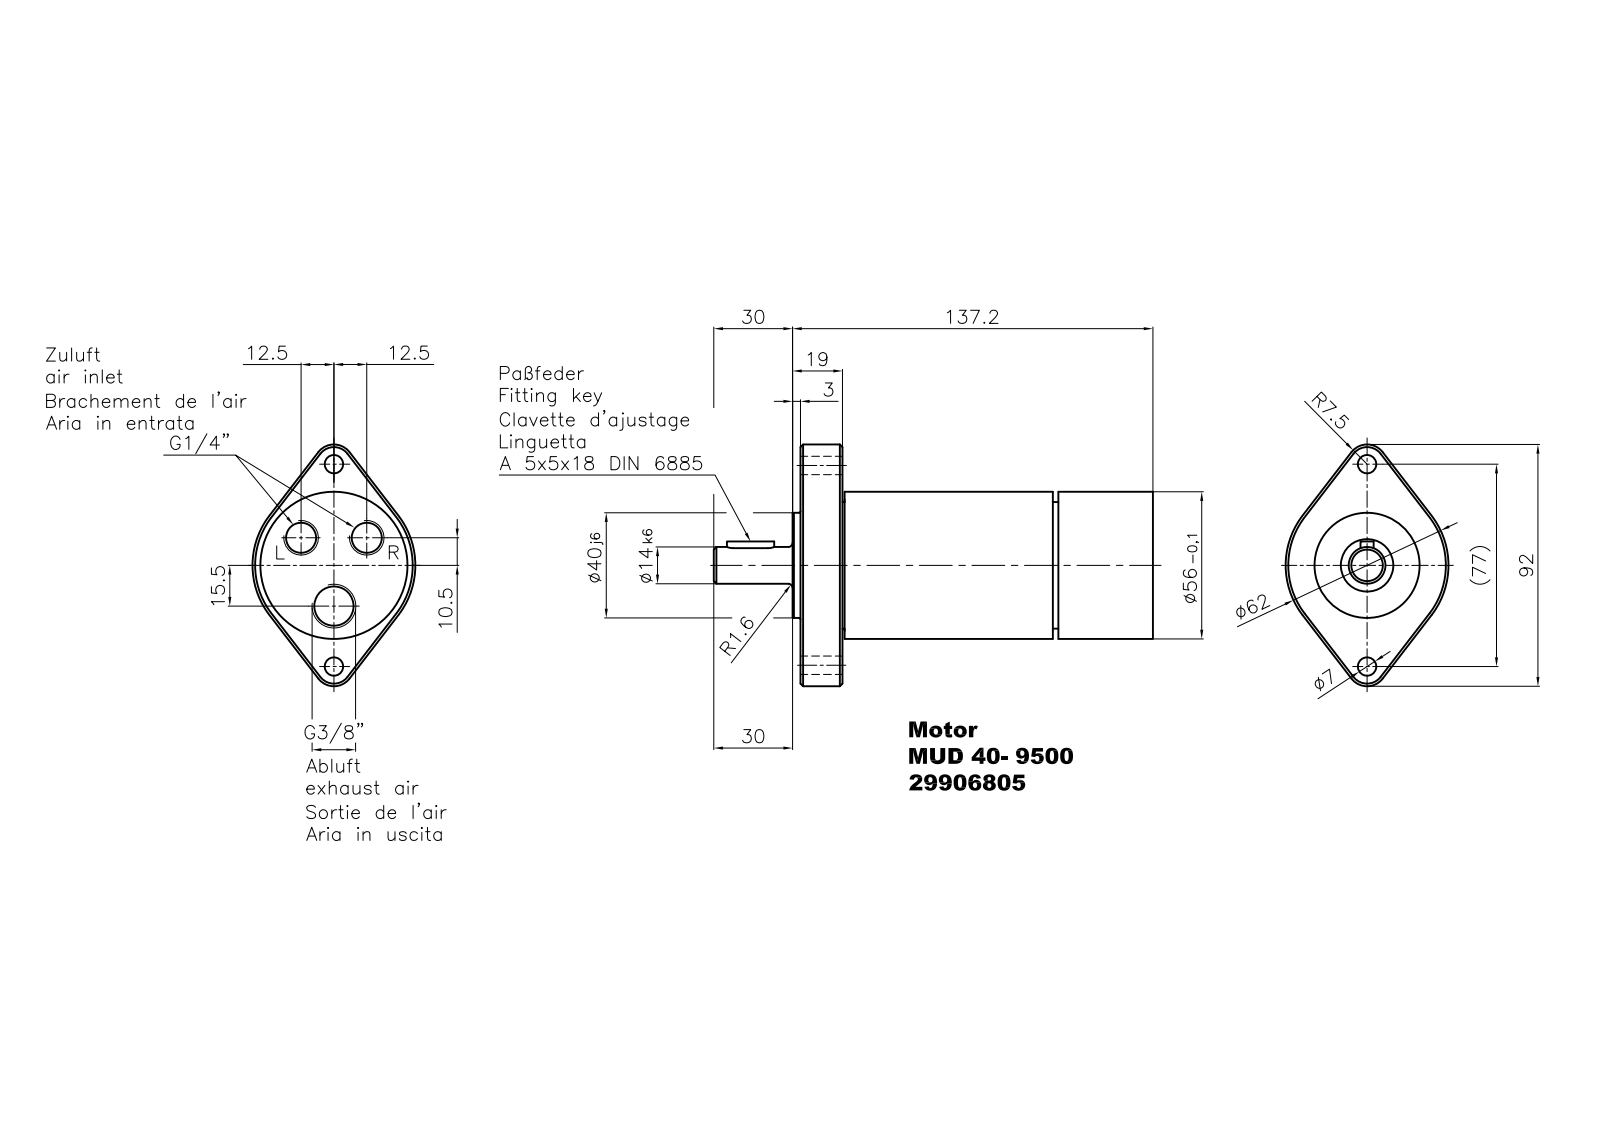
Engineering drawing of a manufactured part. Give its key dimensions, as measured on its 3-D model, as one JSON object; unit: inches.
{"part_name": "MUD 40-9500_29906805", "step_written_by": "Autodesk Inventor 2008 (CONFIG_CONTROL_DESIGN)", "units": "inches", "bodies": {"solids": 1, "faces": 68, "planar": 29, "cylindrical": 16, "other": 23}, "overall_size": [6.575, 3.622, 2.441], "volume_in3": 21.45, "surface_area_in2": 58.16, "round_bosses_or_shafts": [[2.205, 1], [2.084, 1], [1.575, 1], [0.781, 1], [0.551, 1]], "partial_cylinders_radius": [[0.098, 2], [0.295, 2], [0.433, 1], [0.906, 1], [1.22, 1]], "face_to_face_distances": [5.283, 0.63, 4.654, 0.118, 0.748, 5.402, 4.892, 4.774, 4.144, 0.509]}
